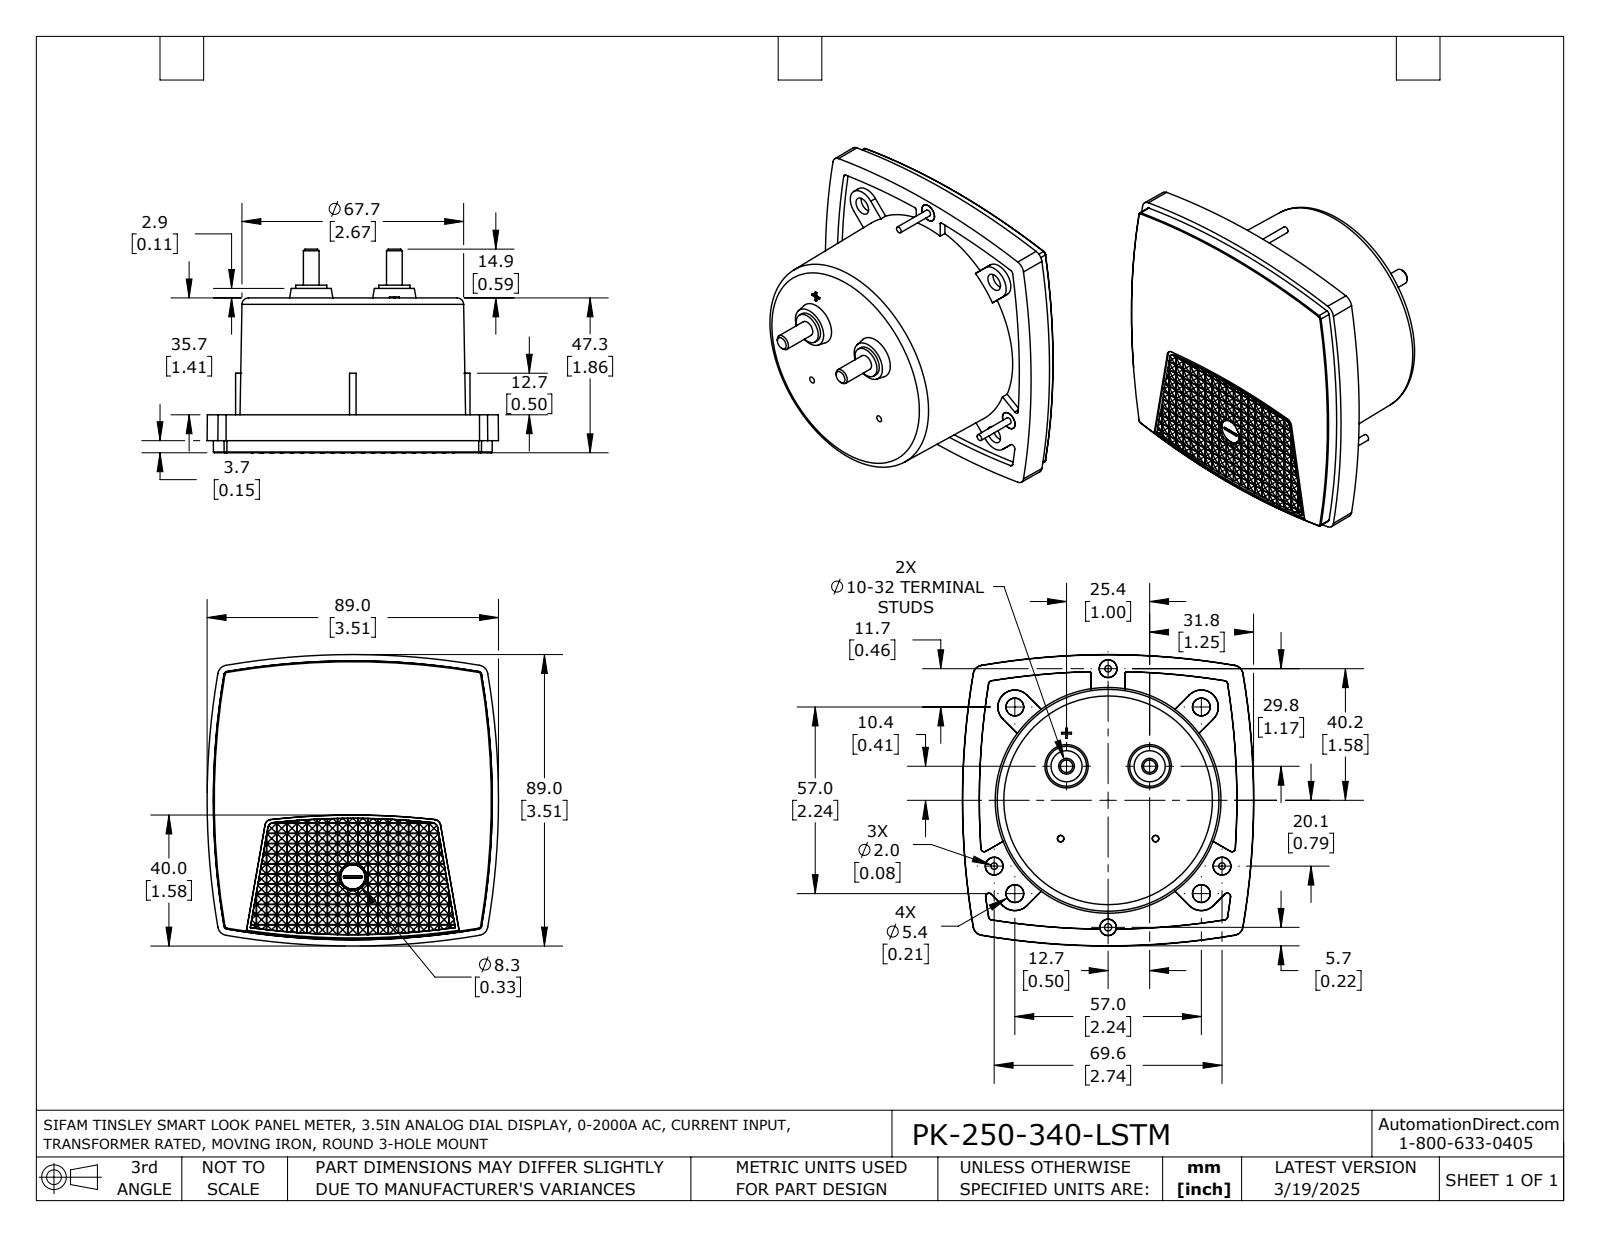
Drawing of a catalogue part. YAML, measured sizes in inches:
part_name: "PK-250-340-LSTM"
step_written_by: "SolidWorks 2021 (AUTOMOTIVE_DESIGN)"
units: inches
bodies: {solids: 1, faces: 1078, planar: 950, cylindrical: 23, other: 105}
overall_size: [3.505, 3.505, 2.453]
volume: 12.99
surface_area: 44.29
round_holes:
  - {diameter: 0.087, count: 1}
round_bosses_or_shafts:
  - {diameter: 0.213, count: 3}
  - {diameter: 0.079, count: 3}
  - {diameter: 0.374, count: 2}
  - {diameter: 0.189, count: 2}
partial_cylinders:
  - {radius: 8.961, count: 1}
face_to_face_distances: [1.862, 1.406, 0.457, 0.079, 1.484, 0.378, 0.024, 0.096, 0.072, 0.12]
